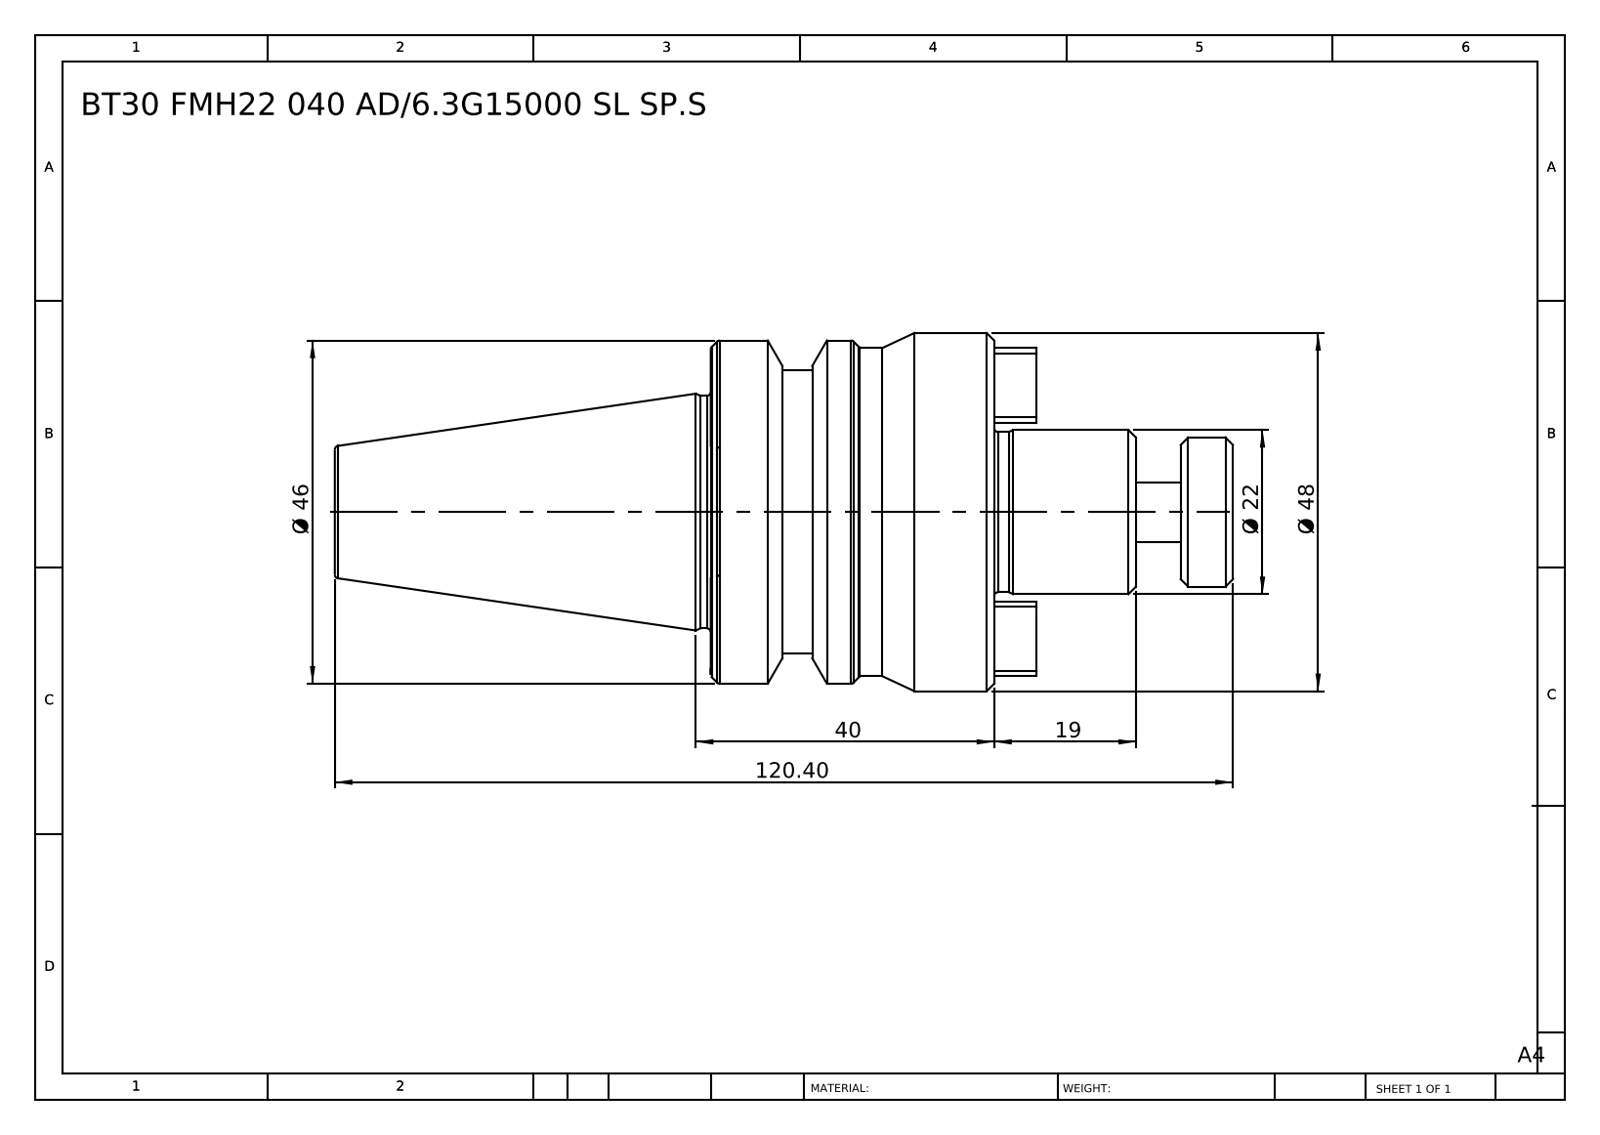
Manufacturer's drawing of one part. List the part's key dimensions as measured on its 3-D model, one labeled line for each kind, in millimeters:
Part name (STEP PRODUCT): BT30 FMH22 040 AD-6.3G15000 SL SP
STEP written by: SolidWorks 2014 (CONFIG_CONTROL_DESIGN)
Units: millimetres
Bodies: 1 solid, 91 faces (27 planar, 20 cylindrical, 44 other)
Overall size (bounding box): 120.4 × 48 × 48
Volume: 97 136 mm³ · Surface area: 15 719 mm²
Round bosses / shafts (diameter × count): ⌀48 ×1, ⌀46 ×1, ⌀44 ×1, ⌀38 ×1, ⌀31.2 ×1, ⌀22 ×1, ⌀21.5 ×1, ⌀20 ×1
Main face-to-face distances: 38, 19, 57, 13, 32, 70, 120.4, 107.4, 88.4, 50.4
